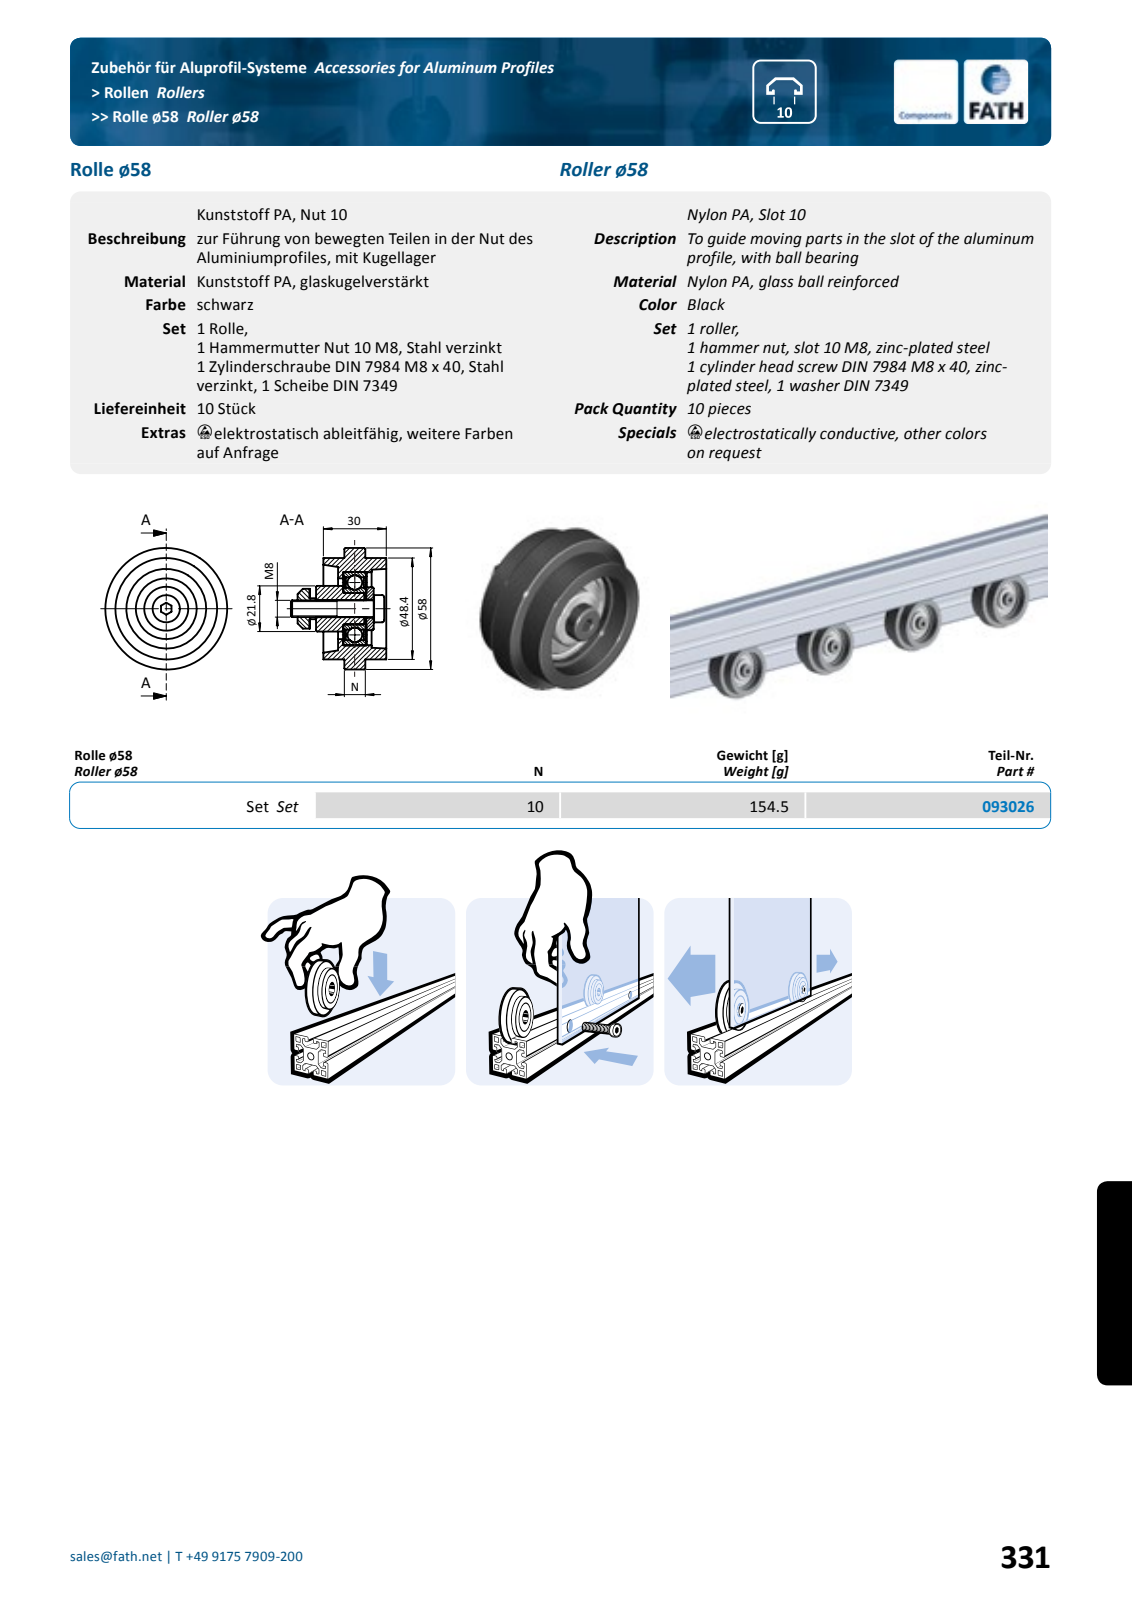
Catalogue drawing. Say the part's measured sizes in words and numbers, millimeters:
The part is named "fath_093026_1; fath_093026_2; fath_093026_3; fath_093026_4 (+8 more)". Its 3-D file was written by "Spatial InterOp 3D (automotive_design)". It is 12 solids with 252 faces: 128 planar, 46 cylindrical and 78 other. Overall it measures 58 by 58 by 45.5 millimeters. Its volume is 44 151 cubic millimeters and its surface area 21 573 square millimeters. Round holes: 1 of diameter 6.8, 1 of diameter 8.1, 1 of diameter 8.7, 1 of diameter 15, 1 of diameter 20, 1 of diameter 29, 1 of diameter 34.8, 1 of diameter 35. Round bosses or shafts: 1 of diameter 58, 1 of diameter 48.4, 1 of diameter 30, 1 of diameter 21.8, 1 of diameter 20.5, 1 of diameter 13, 1 of diameter 8. Partial cylindrical surfaces (rounded edges, fillets, slot ends): 1 of radius 5, 1 of radius 9.5. The main face-to-face distances are 10, 10.5, 20, 0.5, 13, 9.5, 19.3, 1, 20.5, 23.
